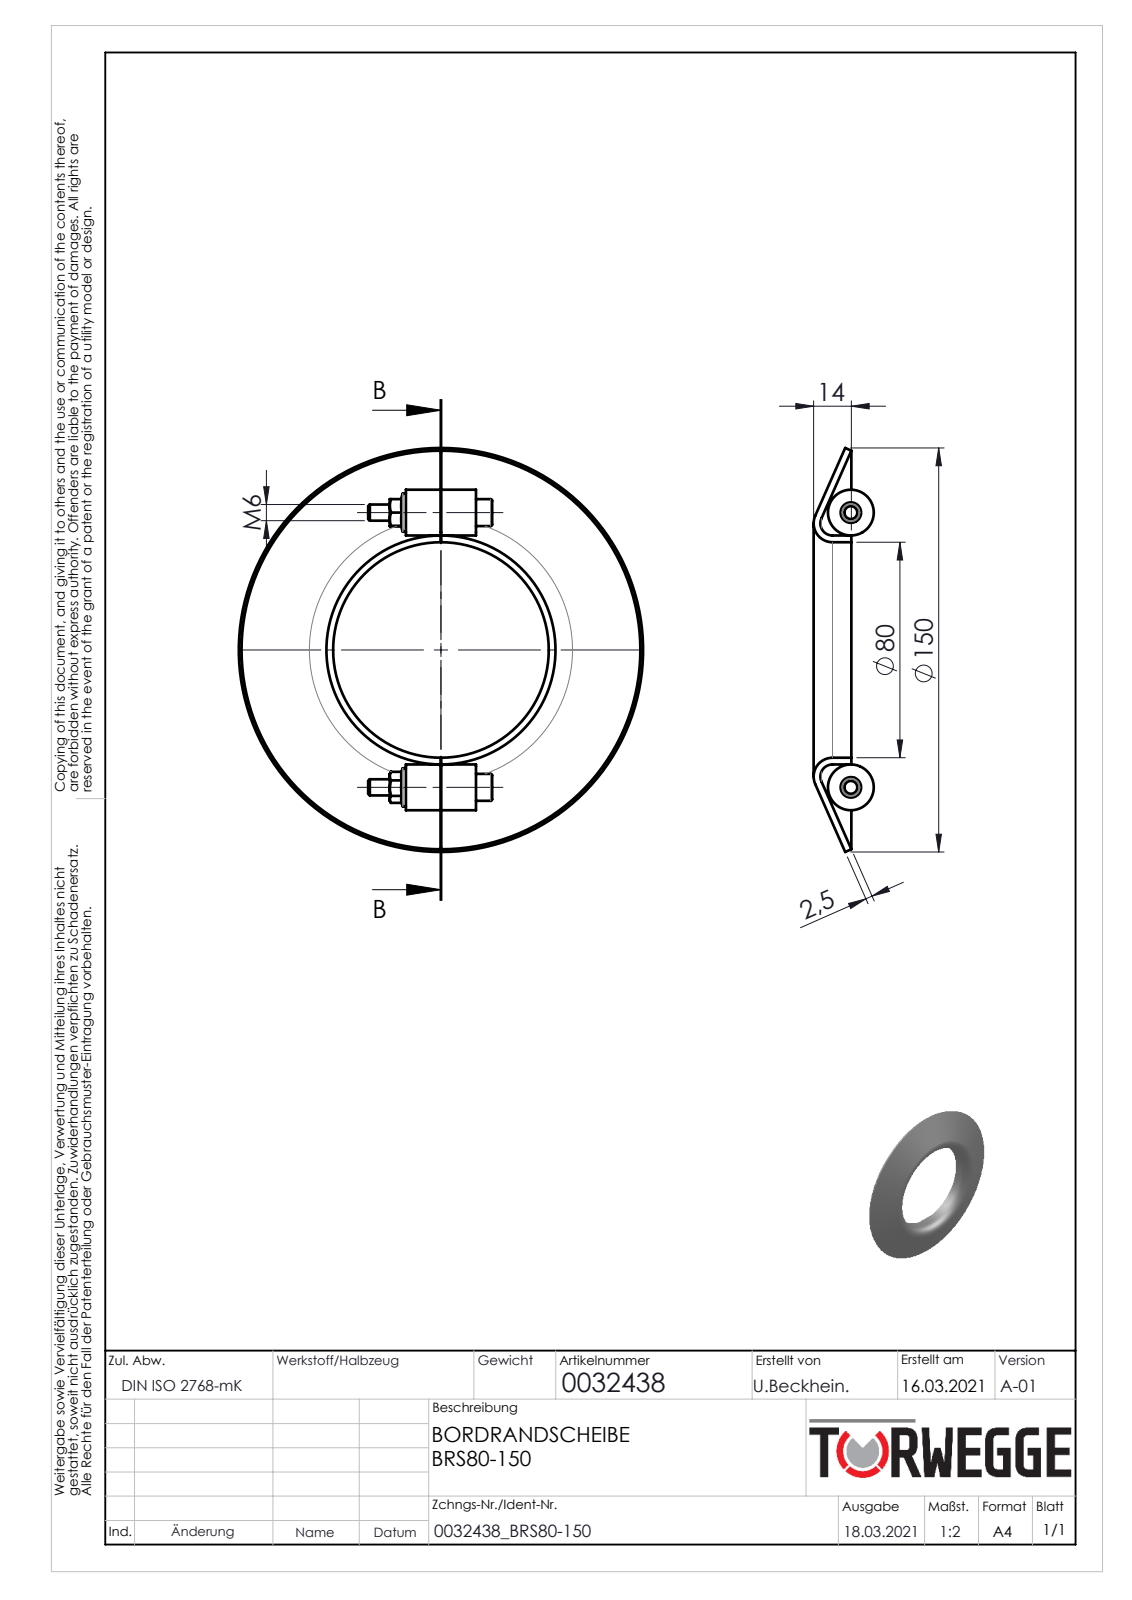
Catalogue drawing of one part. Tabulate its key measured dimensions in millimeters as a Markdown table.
| quantity | value |
| --- | --- |
| part name | 0032438 |
| STEP written by | SolidWorks 2020 (AUTOMOTIVE_DESIGN) |
| units | millimeters |
| bodies | 10 solids, 172 faces (60 planar, 36 cylindrical, 76 other) |
| overall size | 150 × 150 × 22.32 |
| volume | 52 739 mm³ |
| surface area | 42 526 mm² |
| round holes (diameter × count) | 5 × 2, 7.6 × 2, 80 × 1 |
| round bosses / shafts (diameter × count) | 17 × 2, 14.2 × 2, 10 × 2, 6 × 2, 85 × 1 |
| main face-to-face distances | 13, 26, 6, 19, 32, 10, 38, 5, 9.99, 8 |
| hole center spacings | 102 |
